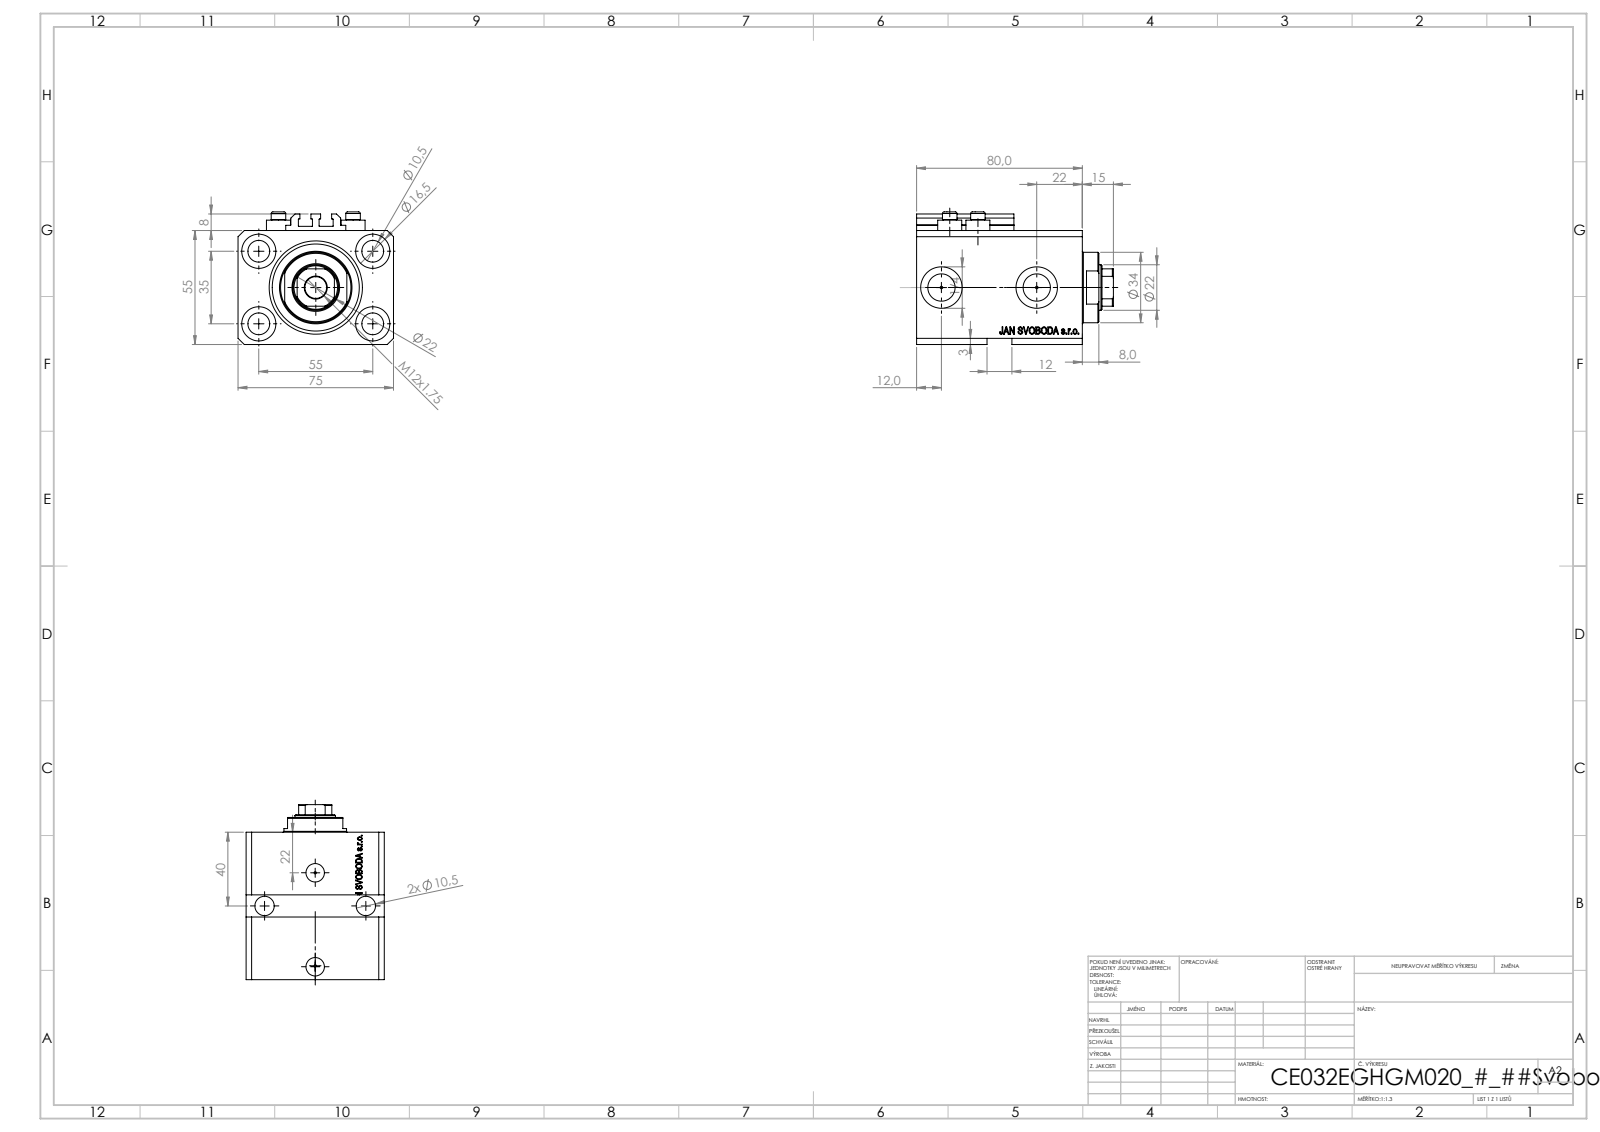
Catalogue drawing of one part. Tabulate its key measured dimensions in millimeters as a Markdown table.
| quantity | value |
| --- | --- |
| part name | V250CE_VC_E; ALLEN BOLT V250CE; V250CE_C_VCP; V250CE_E_Body |
| STEP written by | SolidWorks 2019 (CONFIG_CONTROL_DESIGN) |
| units | millimeters |
| bodies | 8 solids, 1064 faces (514 planar, 126 cylindrical, 424 other) |
| overall size | 95 × 75 × 64 |
| volume | 283 894 mm³ |
| surface area | 74 463 mm² |
| round holes (diameter × count) | 10.5 × 7, 1.25 × 4, 4 × 4, 16.5 × 4, 10 × 2, 13.16 × 2, 20 × 2, 22 × 1, 32 × 1, 45 × 1 |
| round bosses / shafts (diameter × count) | 11.6 × 4, 7 × 4, 34 × 1 |
| partial cylindrical surfaces (radius × count) | 0.2 × 10, 10.5 × 1 |
| main face-to-face distances | 55, 75, 15, 80, 65, 3, 55.1, 9.9, 70.1, 54 |
| hole center spacings | 32.6, 55, 13.6, 14.09, 19.89, 20.12, 25.81, 28.48 |
